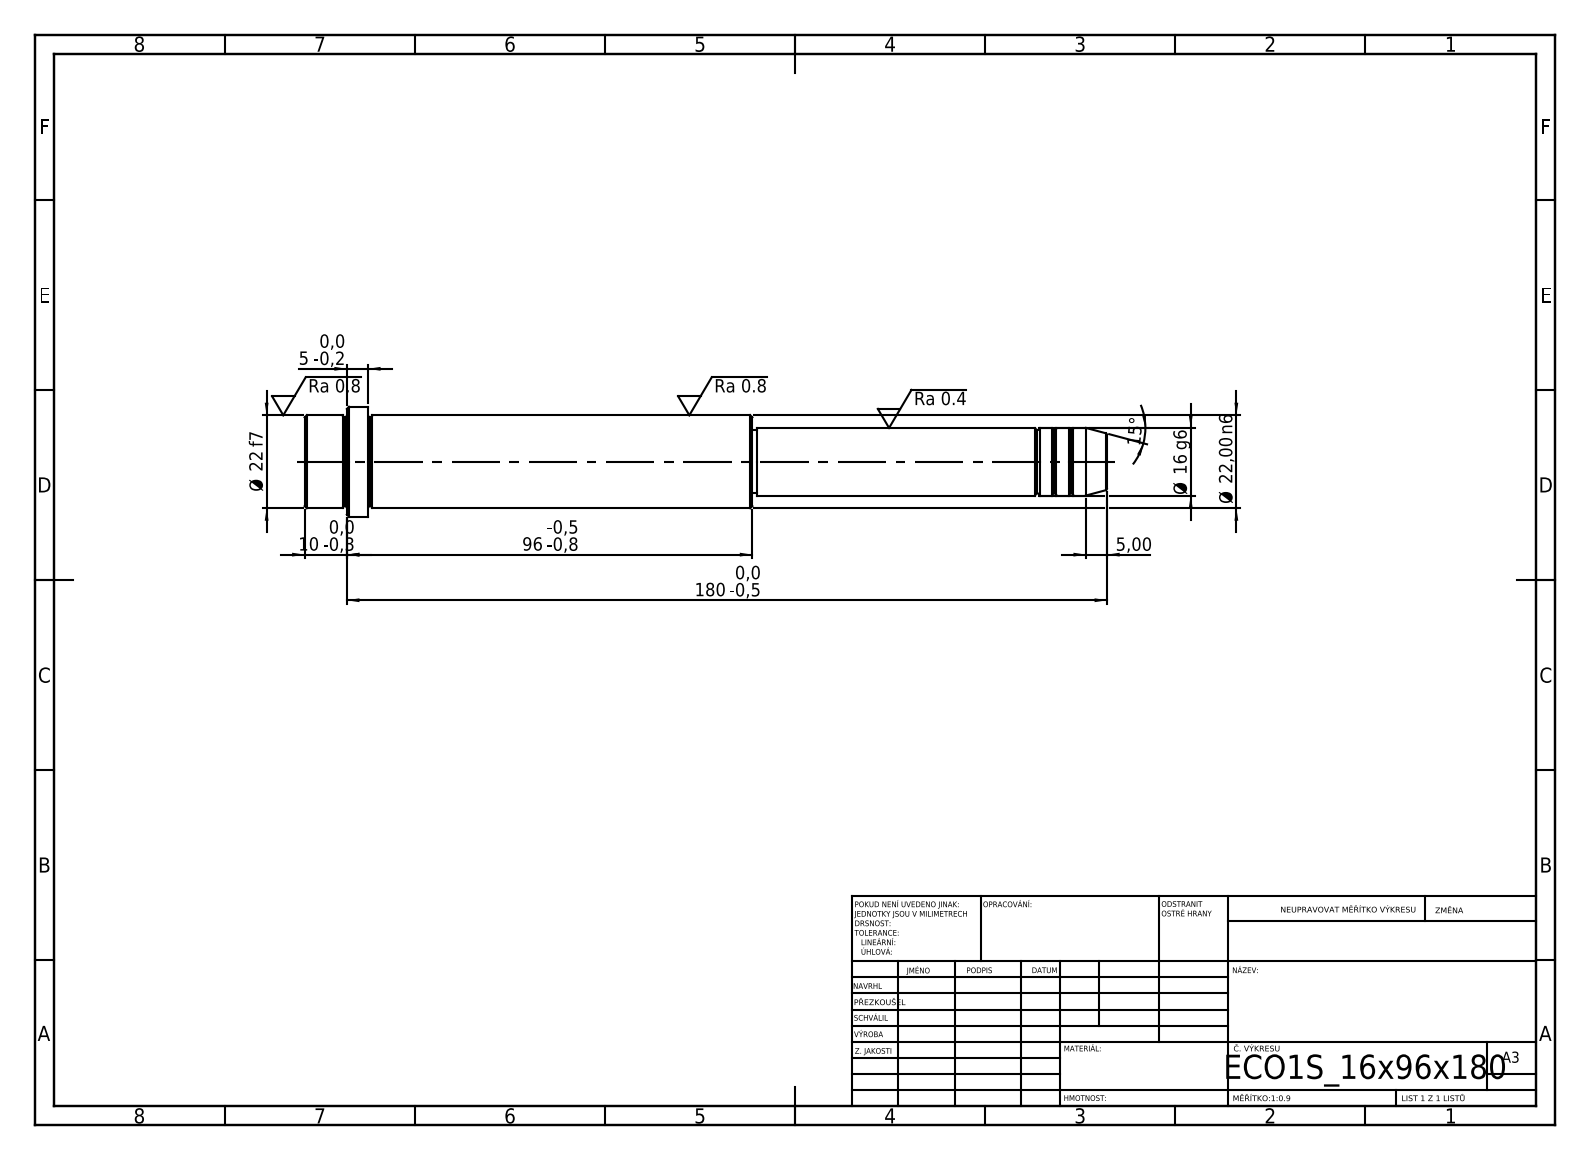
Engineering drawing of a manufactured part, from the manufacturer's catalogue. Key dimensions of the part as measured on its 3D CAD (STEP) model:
STEP written by: SolidWorks 2019 (CONFIG_CONTROL_DESIGN)
Units: millimetres
Bodies: 1 solid, 52 faces (6 planar, 16 cylindrical, 30 other)
Overall size (bounding box): 190 × 26 × 26
Volume: 57 615 mm³ · Surface area: 12 723 mm²
Round bosses / shafts (diameter × count): ⌀26 ×1, ⌀22 ×1, ⌀16 ×1, ⌀15 ×1
Main face-to-face distances: 106, 91, 15, 84, 175, 190, 180, 96, 5, 10
